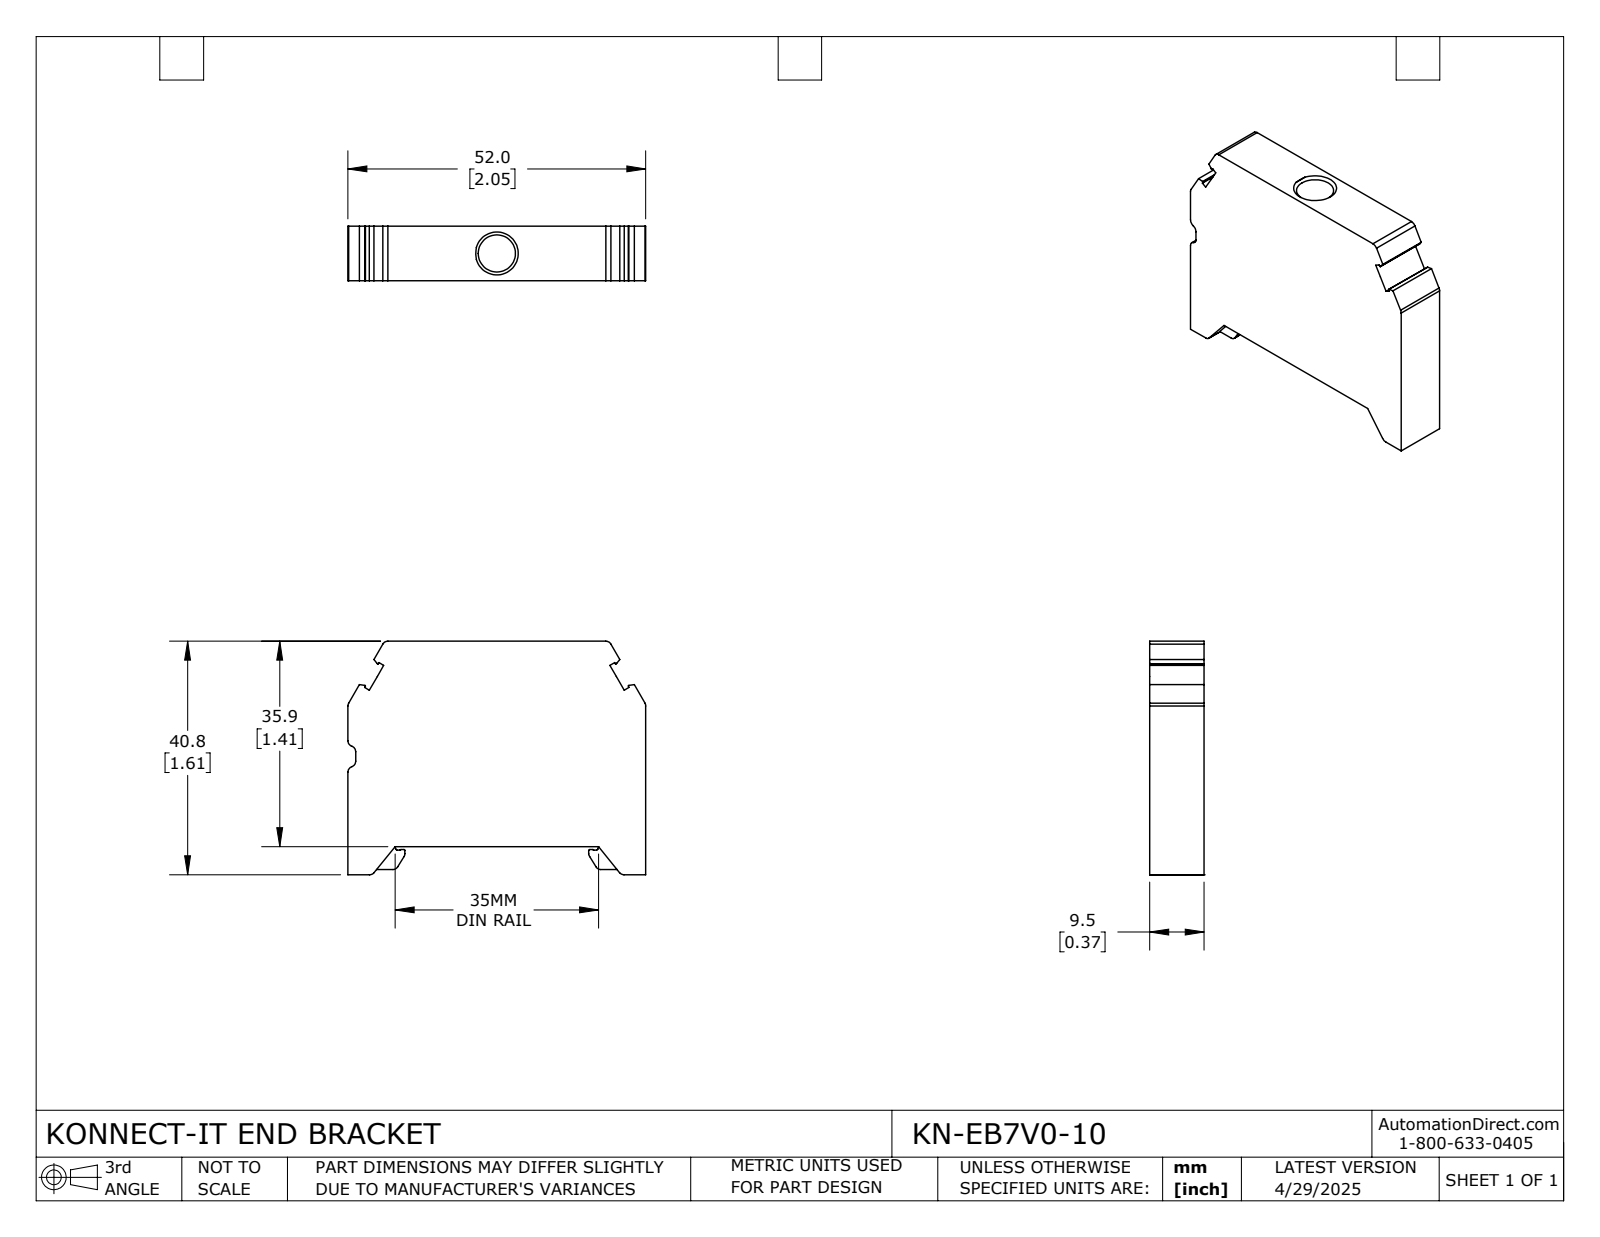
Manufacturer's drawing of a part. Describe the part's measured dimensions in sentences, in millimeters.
The part is named "KN-EB7V0-10". Its 3-D file was written by "SolidWorks 2024 (CONFIG_CONTROL_DESIGN)". It is 1 solid with 105 faces: 59 planar, 43 cylindrical and 3 other. Overall it measures 52 by 40.77 by 9.5 millimeters. Its volume is 17 418 cubic millimeters and its surface area 5 580 square millimeters. Partial cylindrical surfaces (rounded edges, fillets, slot ends): 14 of radius 1, 8 of radius 0.1, 4 of radius 0.2, 2 of radius 2.94. The main face-to-face distances are 9.5, 35.85, 52, 1.99, 4.92, 40.77, 2.2, 7.3, 3.2, 6.3.
